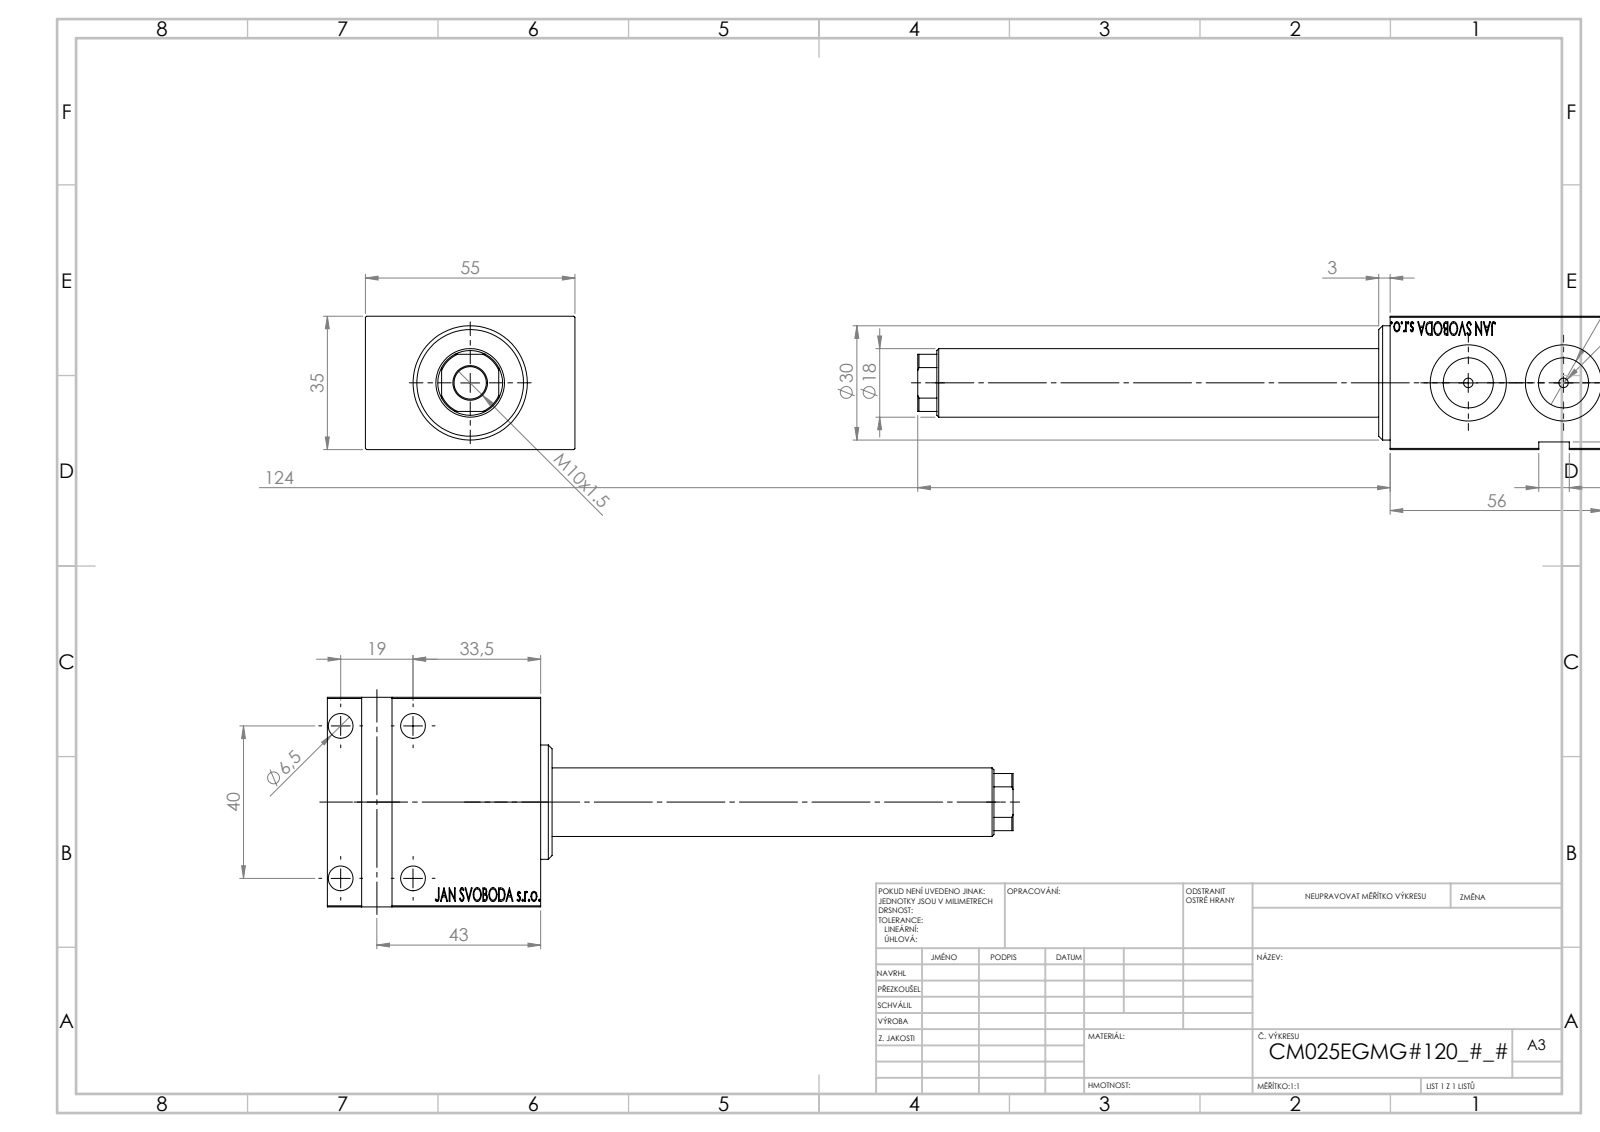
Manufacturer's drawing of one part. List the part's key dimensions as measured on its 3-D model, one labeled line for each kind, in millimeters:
Part name (STEP PRODUCT): V450CM_E_Body; V450CM_VC_B; V450CM_E_VCP
STEP written by: SolidWorks 2019 (CONFIG_CONTROL_DESIGN)
Units: millimetres
Bodies: 3 solids, 861 faces (411 planar, 56 cylindrical, 394 other)
Overall size (bounding box): 180 × 55 × 35
Volume: 128 514 mm³ · Surface area: 37 364 mm²
Round holes (diameter × count): ⌀6.5 ×4, ⌀2.5 ×2, ⌀10.5 ×2, ⌀13.16 ×2, ⌀20 ×2, ⌀8.5 ×1, ⌀10 ×1, ⌀13.5 ×1, ⌀14.5 ×1, ⌀25 ×1, ⌀27 ×1
Round bosses / shafts (diameter × count): ⌀30 ×1, ⌀18 ×1
Partial cylindrical surfaces — rounded edges, fillets, slot ends (radius × count): R5.25 ×2, R8.5 ×1
Main face-to-face distances: 35, 56, 55, 5, 51, 34.4, 16.6, 39.4, 42, 3
Hole centre spacings: 19, 40, 44.28, 25
